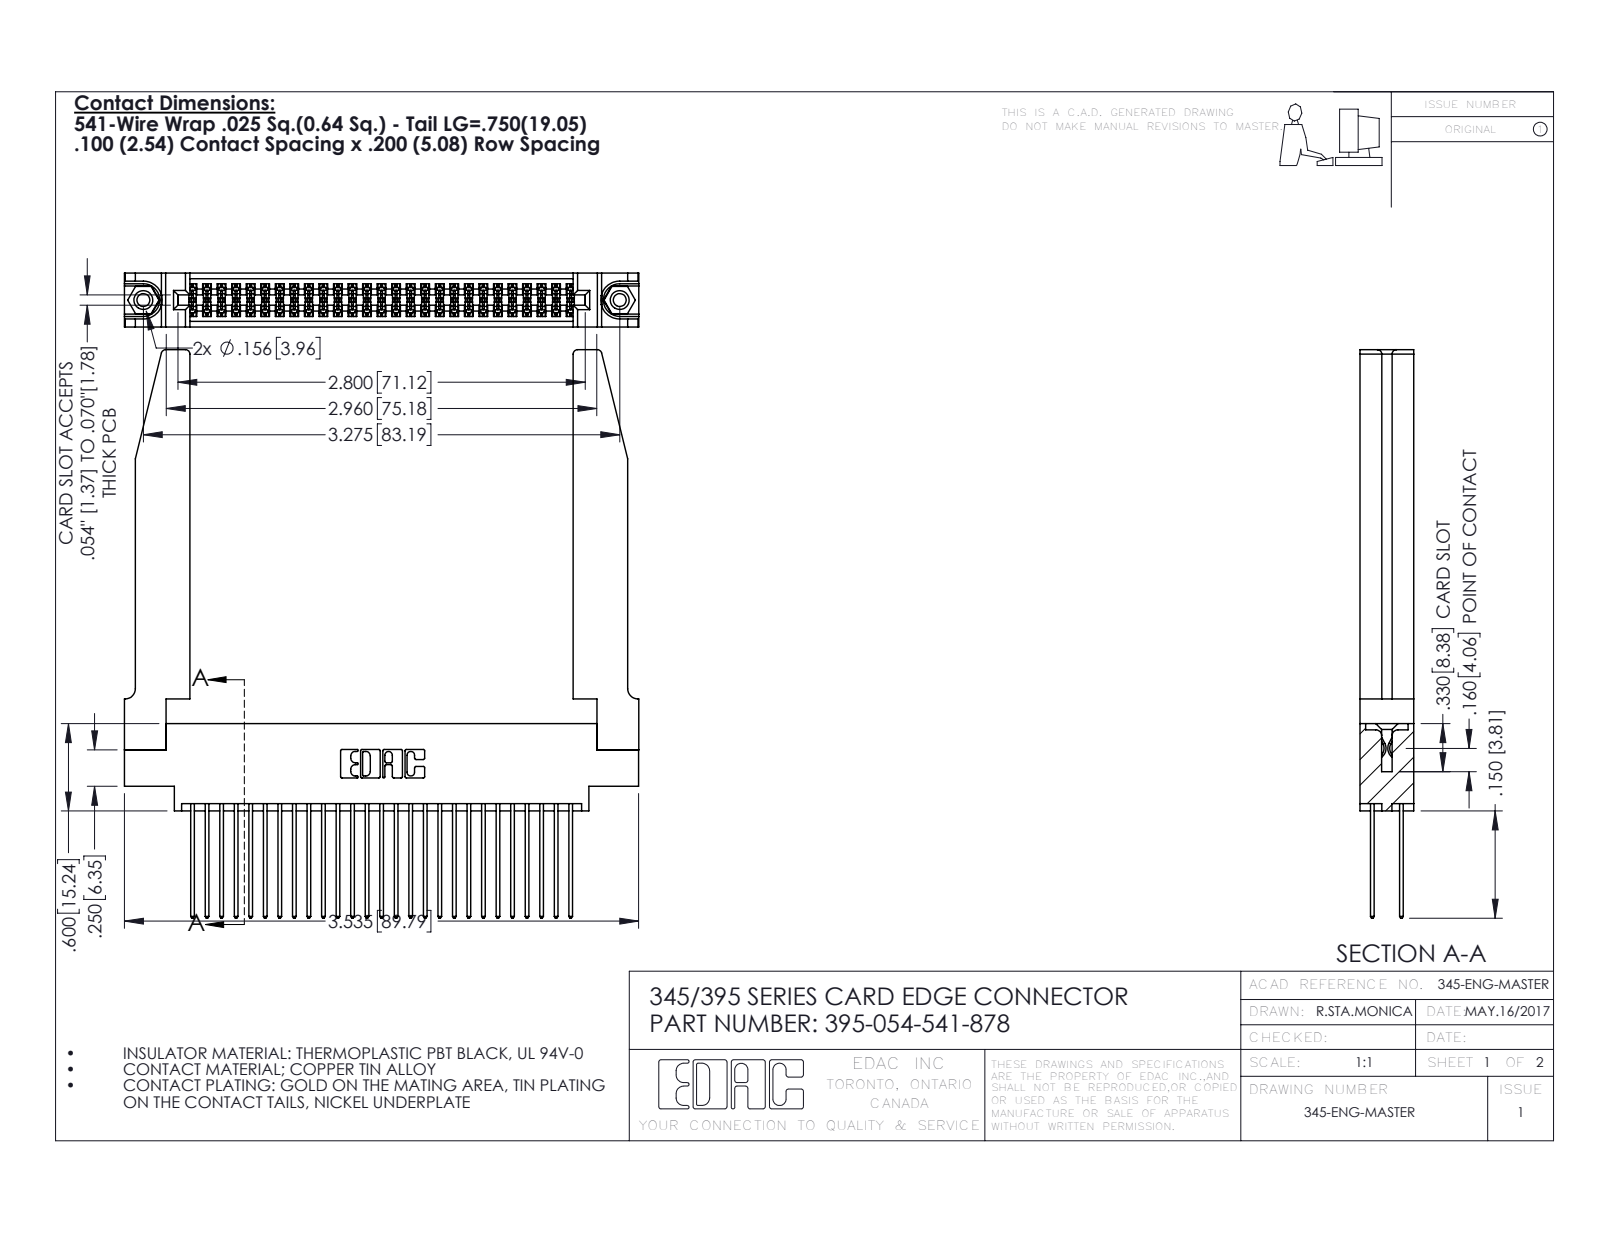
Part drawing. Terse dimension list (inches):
name: 345-292-001_345-293-141; 345-250-001_345-250-001-102; 395-054-541-878; 345-220-078_345-220-078 (+1 more)
written by: SolidWorks 2016 (CONFIG_CONTROL_DESIGN)
unit: in
bodies: 59 solids, 3064 faces (2008 planar, 1004 cylindrical, 52 other)
size: 3.907 × 3.536 × 0.37
volume: 1.01 in³; area: 32.75 in²
holes: 2× ⌀0.089, 2× ⌀0.125, 2× ⌀0.156, 1× ⌀0.064
bosses: 2× ⌀0.155
rounds: 81× R0.006, 54× R0.01, 22× R0.01, 8× R0.03, 6× R0.007, 6× R0.031, 3× R0.026, 2× R0.014
face distances: 0.37, 0.072, 0.298, 0.098, 0.272, 0.025, 0.2, 0.225, 0.175, 0.148
hole spacings: 0.27, 3.04, 3.275
